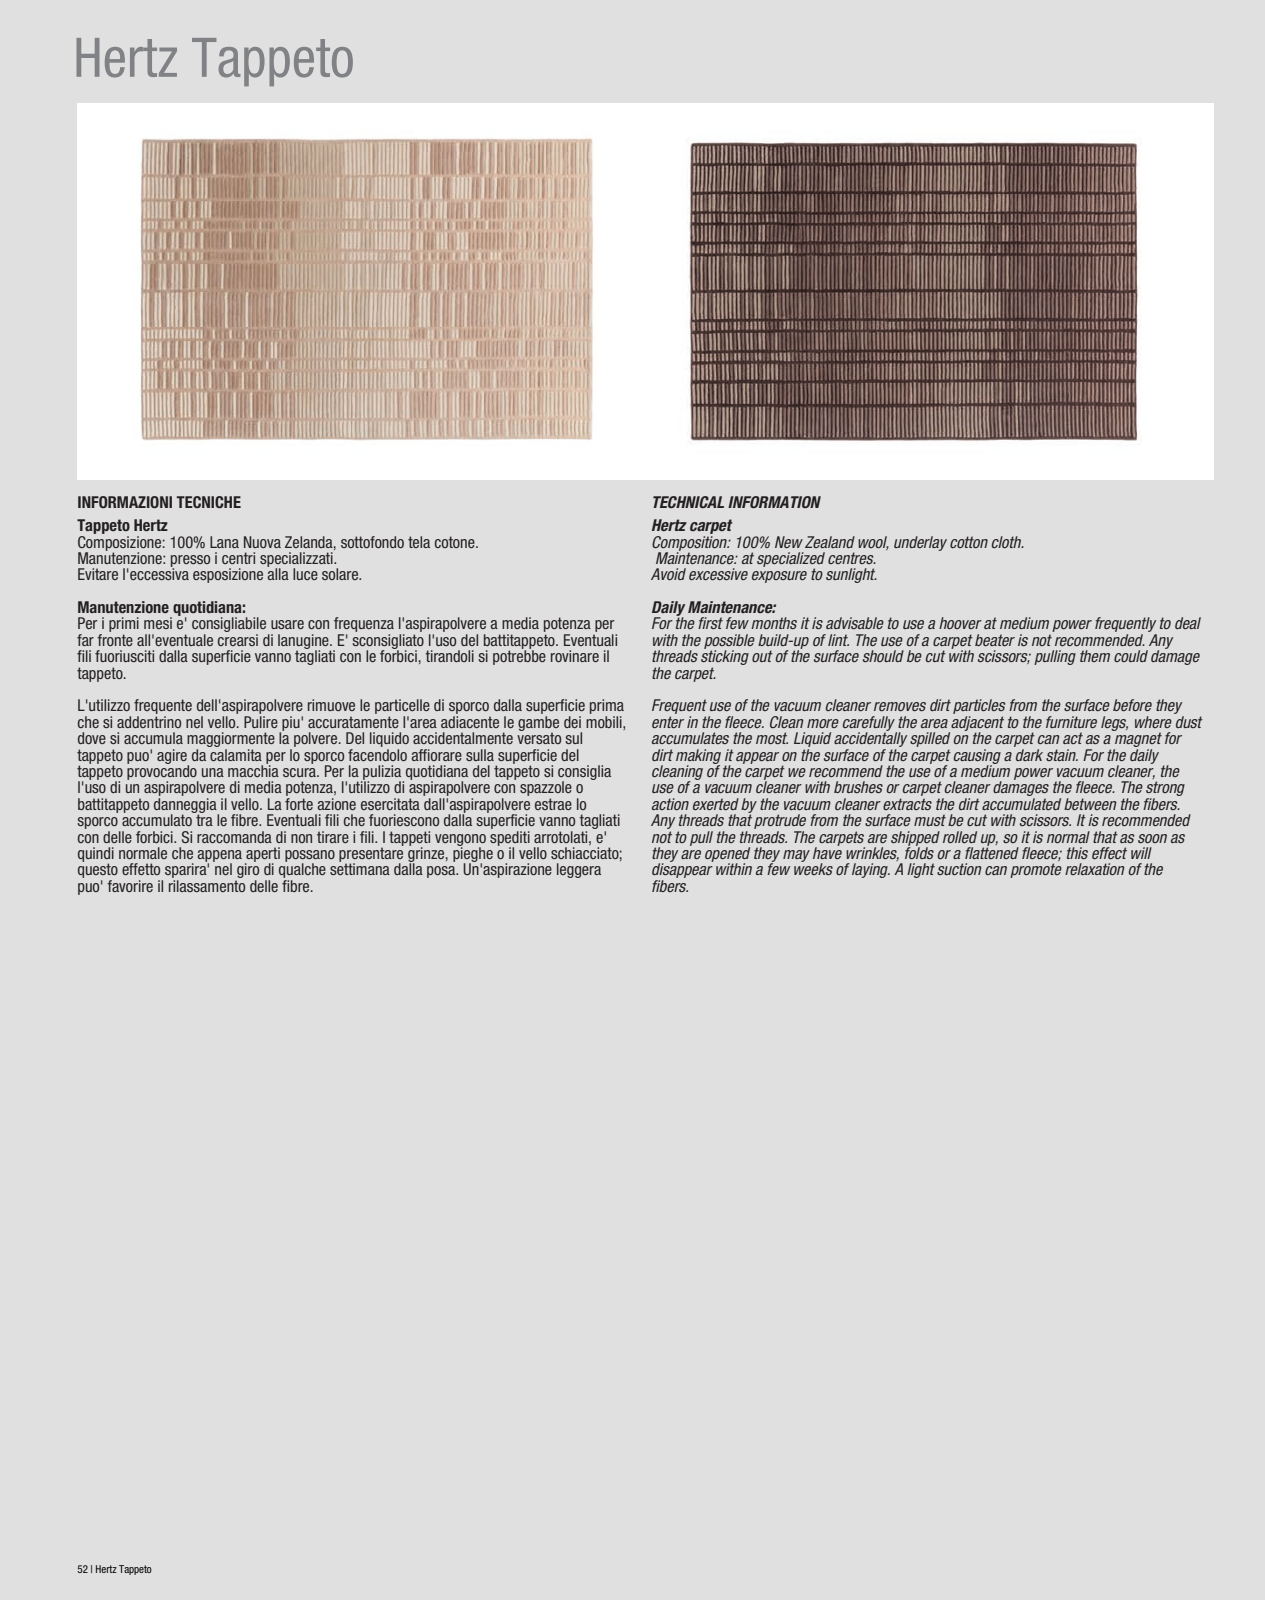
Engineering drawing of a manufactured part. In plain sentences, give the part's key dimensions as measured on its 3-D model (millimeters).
The part is named "094.ALISTAIR PIE; ALISTAIR P; 094.ALISTAIR BASE PIE; TUBO INFERIOR PIE (+4 more)". Its 3-D file was written by "SolidWorks 2010 (AUTOMOTIVE_DESIGN)". It is 10 solids with 478 faces: 279 planar, 167 cylindrical and 32 other. Overall it measures 1299.25 by 300 by 300 millimeters. Its volume is 2 362 000 cubic millimeters and its surface area 1 355 000 square millimeters. Round holes: 4 of diameter 11, 3 of diameter 5, 2 of diameter 6, 2 of diameter 10, 1 of diameter 42, 1 of diameter 284, 1 of diameter 292. Round bosses or shafts: 4 of diameter 14, 1 of diameter 300, 1 of diameter 299, 1 of diameter 264, 1 of diameter 45. Partial cylindrical surfaces (rounded edges, fillets, slot ends): 4 of radius 6.5, 4 of radius 50, 4 of radius 65, 2 of radius 2.5, 2 of radius 4, 2 of radius 8, 1 of radius 149. The main face-to-face distances are 5, 3, 8, 789.25, 797.25, 794.25, 792.25, 784.25, 844.25, 841.25. The hole center spacings are 60, 74, 134, 194, 87.64, 120, 268, 340.
